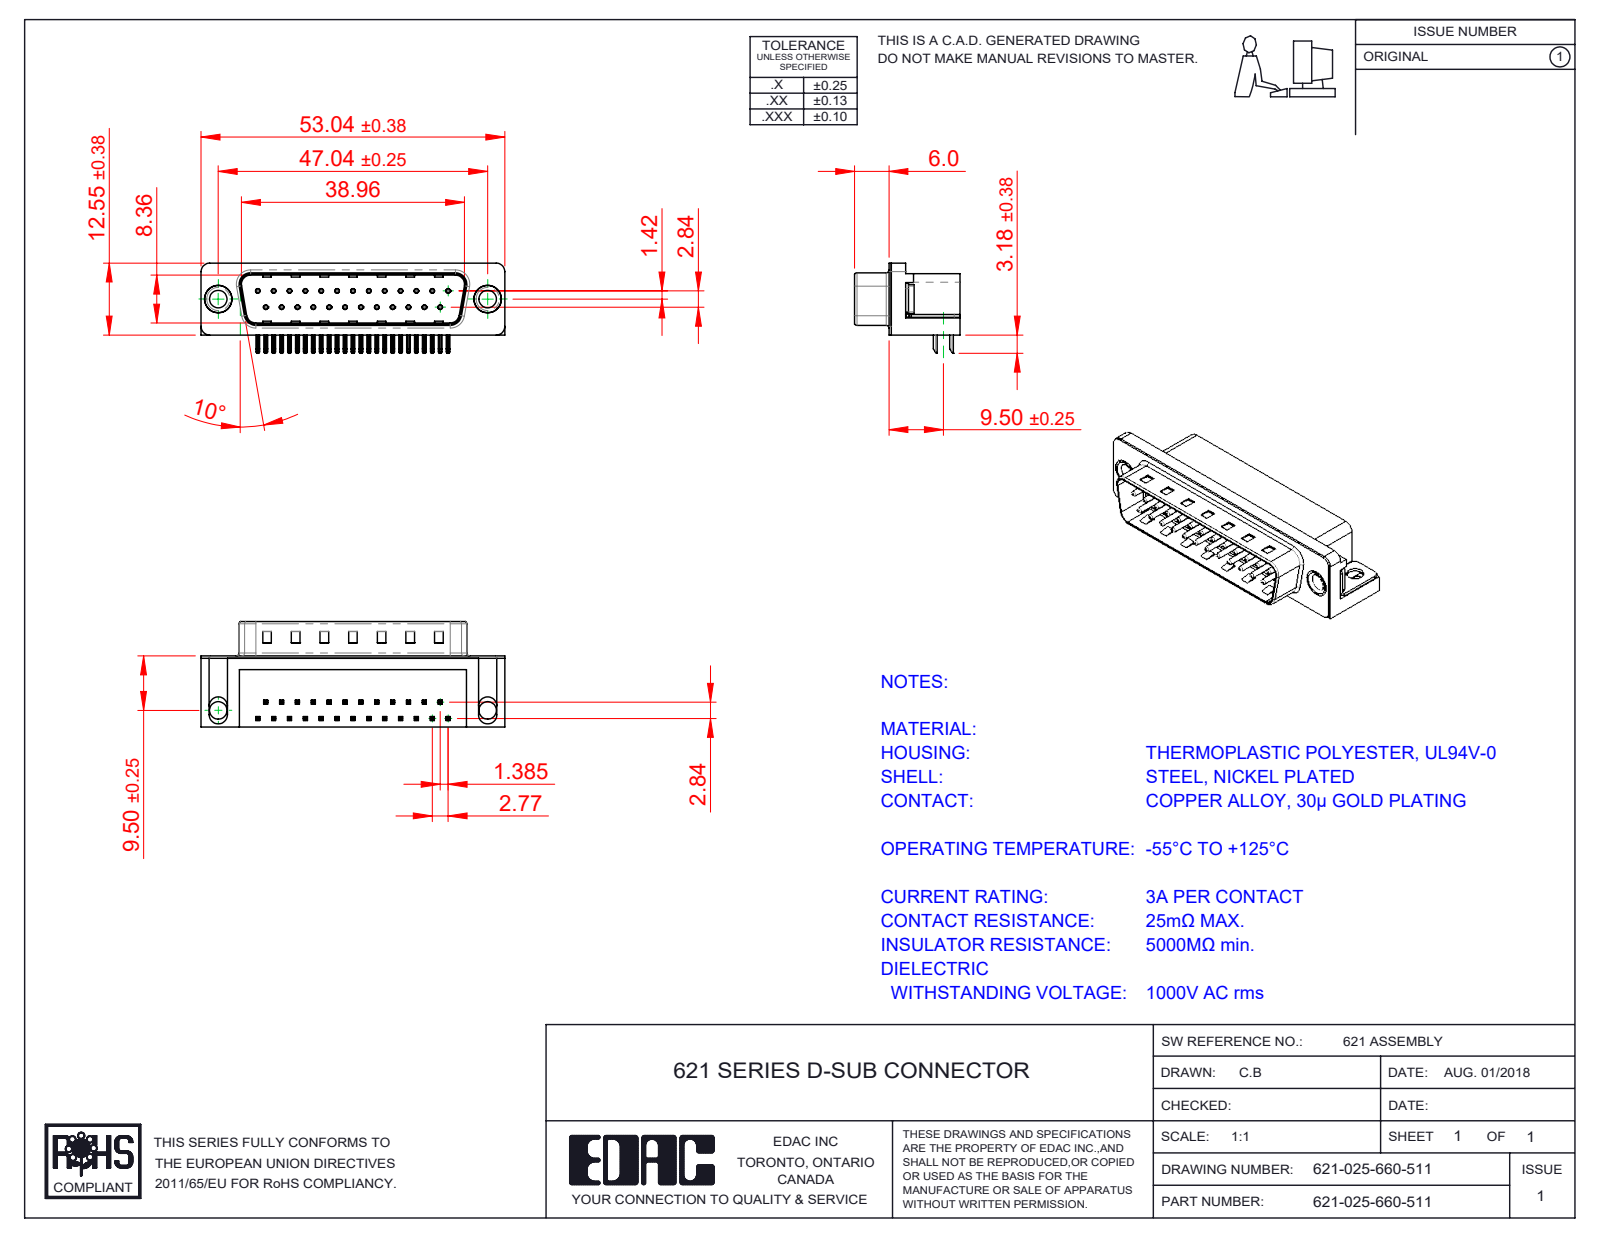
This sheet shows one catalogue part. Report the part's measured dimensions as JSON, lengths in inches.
{"part_name": "621 Shell_25 Socket; 621-025-660-511; 621 Thru Hole Rivet; 621 Housing_25 Socket (+3 more)", "step_written_by": "SolidWorks 2016 (CONFIG_CONTROL_DESIGN)", "units": "inches", "bodies": {"solids": 31, "faces": 2221, "planar": 1403, "cylindrical": 641, "other": 177}, "overall_size": [2.088, 0.724, 0.619], "volume_in3": 0.386, "surface_area_in2": 11.85, "round_holes": [[0.014, 25], [0.031, 25], [0.12, 4], [0.157, 2], [0.189, 2], [0.197, 2]], "round_bosses_or_shafts": [[0.03, 25], [0.193, 2], [0.187, 2], [0.152, 2]], "partial_cylinders_radius": [[0.01, 108], [0.005, 50], [0.039, 16], [0.02, 9], [0.063, 8], [0.059, 7], [0.035, 4], [0.079, 4]], "face_to_face_distances": [0.016, 0.472, 0.407, 0.083, 0.345, 0.412, 0.067, 0.428, 0.488, 0.354], "hole_center_spacings": [0.124, 0.109, 0.218, 0.327, 0.436, 0.545, 0.654, 0.198]}
